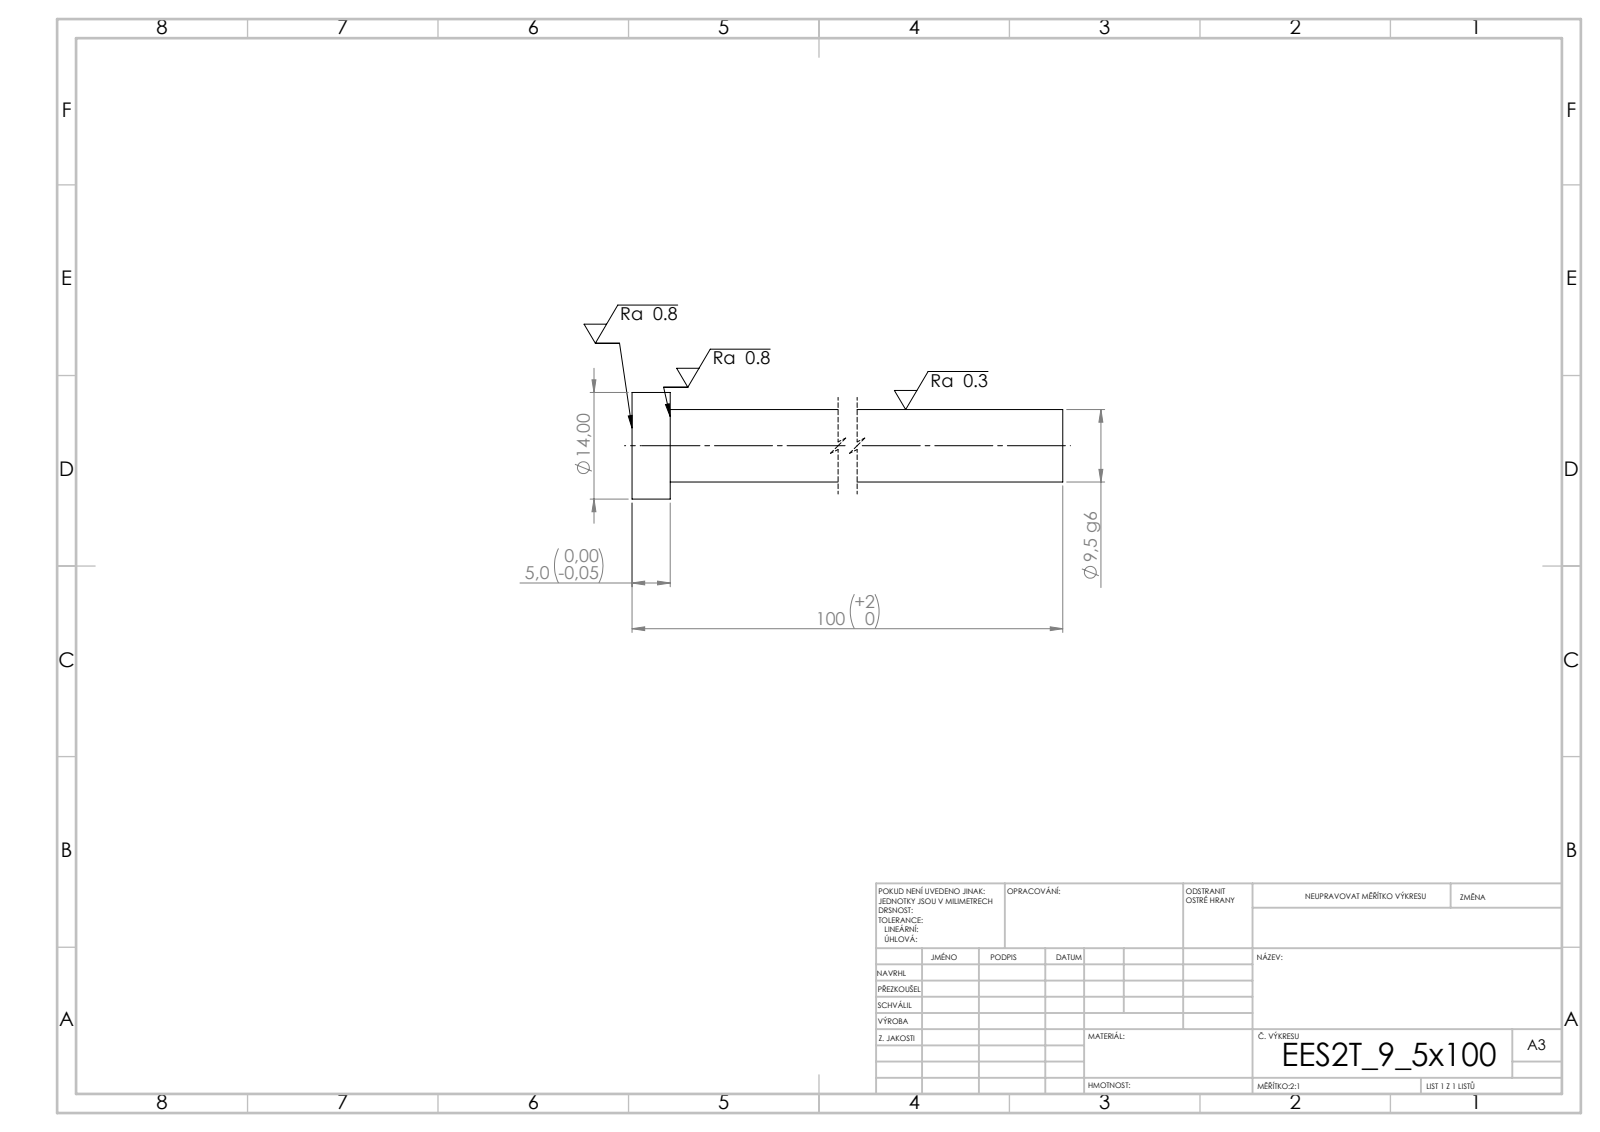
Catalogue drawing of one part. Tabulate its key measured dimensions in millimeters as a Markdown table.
| quantity | value |
| --- | --- |
| STEP written by | SolidWorks 2019 (CONFIG_CONTROL_DESIGN) |
| units | millimeters |
| bodies | 1 solid, 7 faces (3 planar, 4 cylindrical, 0 other) |
| overall size | 100 × 14 × 14 |
| volume | 7 503 mm³ |
| surface area | 3 363 mm² |
| round bosses / shafts (diameter × count) | 14 × 1, 9.5 × 1 |
| main face-to-face distances | 5, 100, 95 |
